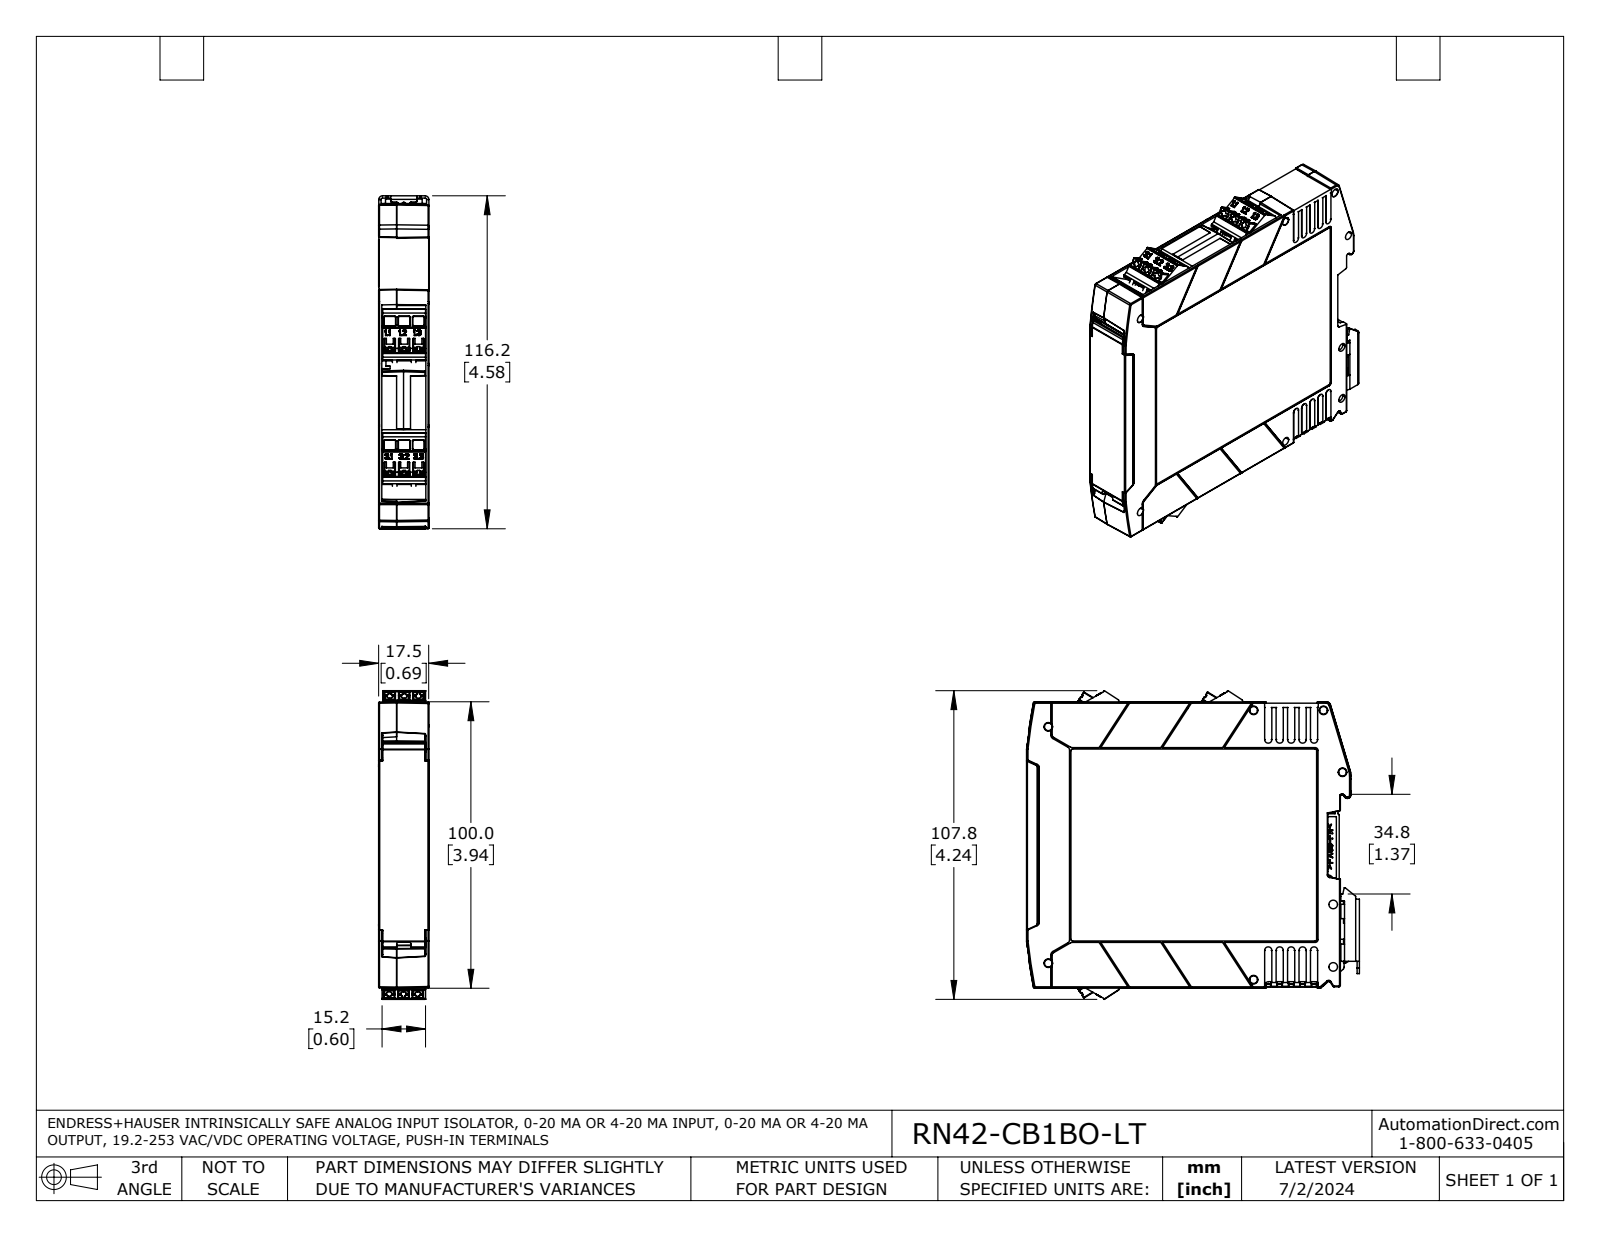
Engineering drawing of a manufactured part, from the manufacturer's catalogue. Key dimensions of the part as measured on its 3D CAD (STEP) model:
Part name (STEP PRODUCT): RN42-CB1BO-LT
STEP written by: SolidWorks 2021 (AUTOMOTIVE_DESIGN)
Units: inches
Bodies: 6 solids, 4355 faces (2900 planar, 793 cylindrical, 662 other)
Overall size (bounding box): 4.577 × 4.242 × 0.693
Volume: 12.22 in³ · Surface area: 112.1 in²
Round holes (diameter × count): ⌀0.059 ×9, ⌀0.11 ×9, ⌀0.118 ×5, ⌀0.135 ×2, ⌀0.009 ×1, ⌀0.14 ×1, ⌀0.184 ×1
Round bosses / shafts (diameter × count): ⌀0.053 ×2
Partial cylindrical surfaces — rounded edges, fillets, slot ends (radius × count): R0.008 ×135, R0.02 ×109, R0.012 ×55, R0.004 ×26, R0.039 ×25, R0.047 ×9, R0.114 ×9, R0.005 ×8
Main face-to-face distances: 0.688, 0.692, 0.052, 0.048, 0.641, 0.043, 0.047, 0.031, 0.039, 0.649
Hole centre spacings: 0.197, 0.394, 1.439, 1.44, 1.426, 1.426, 1.479, 1.48
